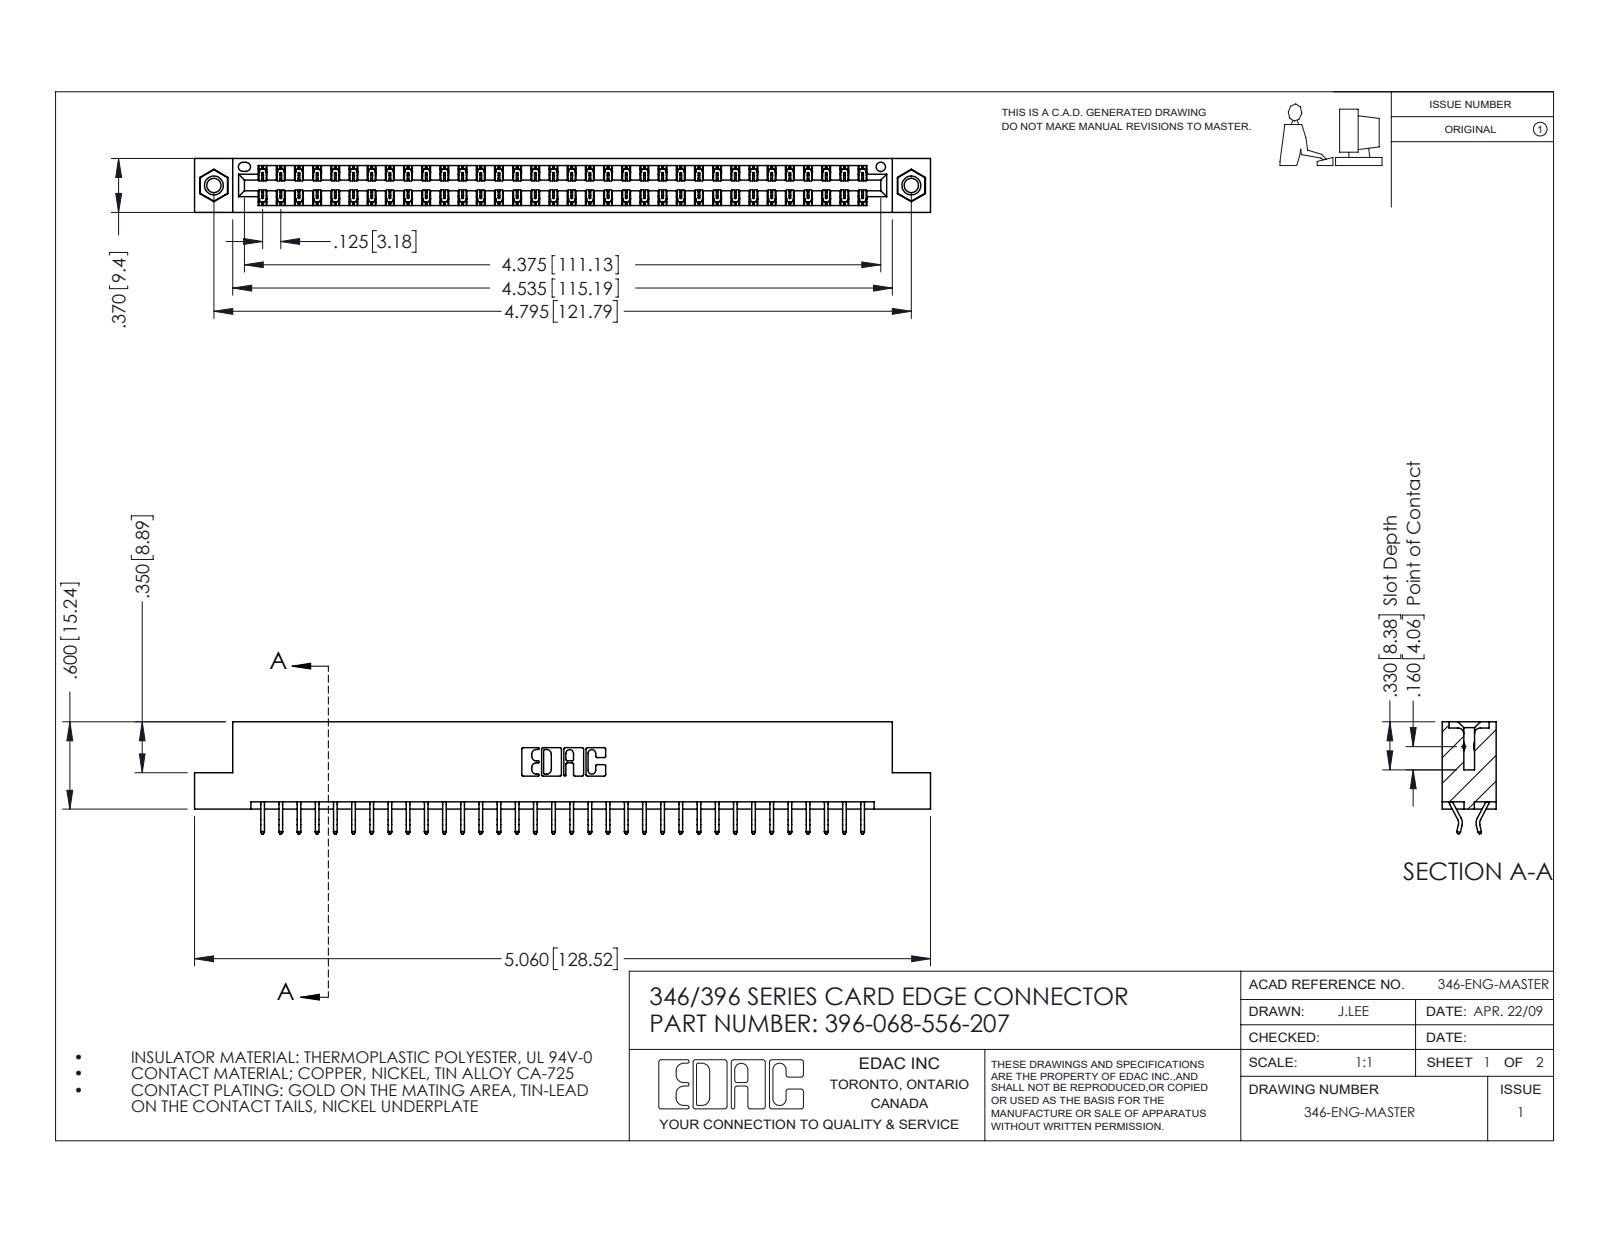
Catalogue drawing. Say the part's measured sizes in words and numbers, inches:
The part is named "345-250-001_345-250-005-103; 345-292-001_556 Tail; 396-068-556-207; 346 Part_Flush Mounting Lugs - 0.156 Dia-TI". Its 3-D file was written by "SolidWorks 2016 (CONFIG_CONTROL_DESIGN)". It is 71 solids with 4126 faces: 2760 planar, 1350 cylindrical and 16 other. Overall it measures 5.06 by 0.77 by 0.37 inches. Its volume is 0.76 cubic inches and its surface area 26.29 square inches. Round holes: 2 of diameter 0.098, 2 of diameter 0.125, 2 of diameter 0.156, 1 of diameter 0.064. Round bosses or shafts: 2 of diameter 0.155. Partial cylindrical surfaces (rounded edges, fillets, slot ends): 102 of radius 0.006, 22 of radius 0.01, 6 of radius 0.007, 6 of radius 0.031, 3 of radius 0.026, 2 of radius 0.01, 2 of radius 0.014, 2 of radius 0.022. The main face-to-face distances are 0.048, 0.322, 0.37, 0.25, 0.025, 0.072, 0.298, 0.275, 0.148, 0.222. The hole center spacings are 0.246, 4.587, 4.795.
